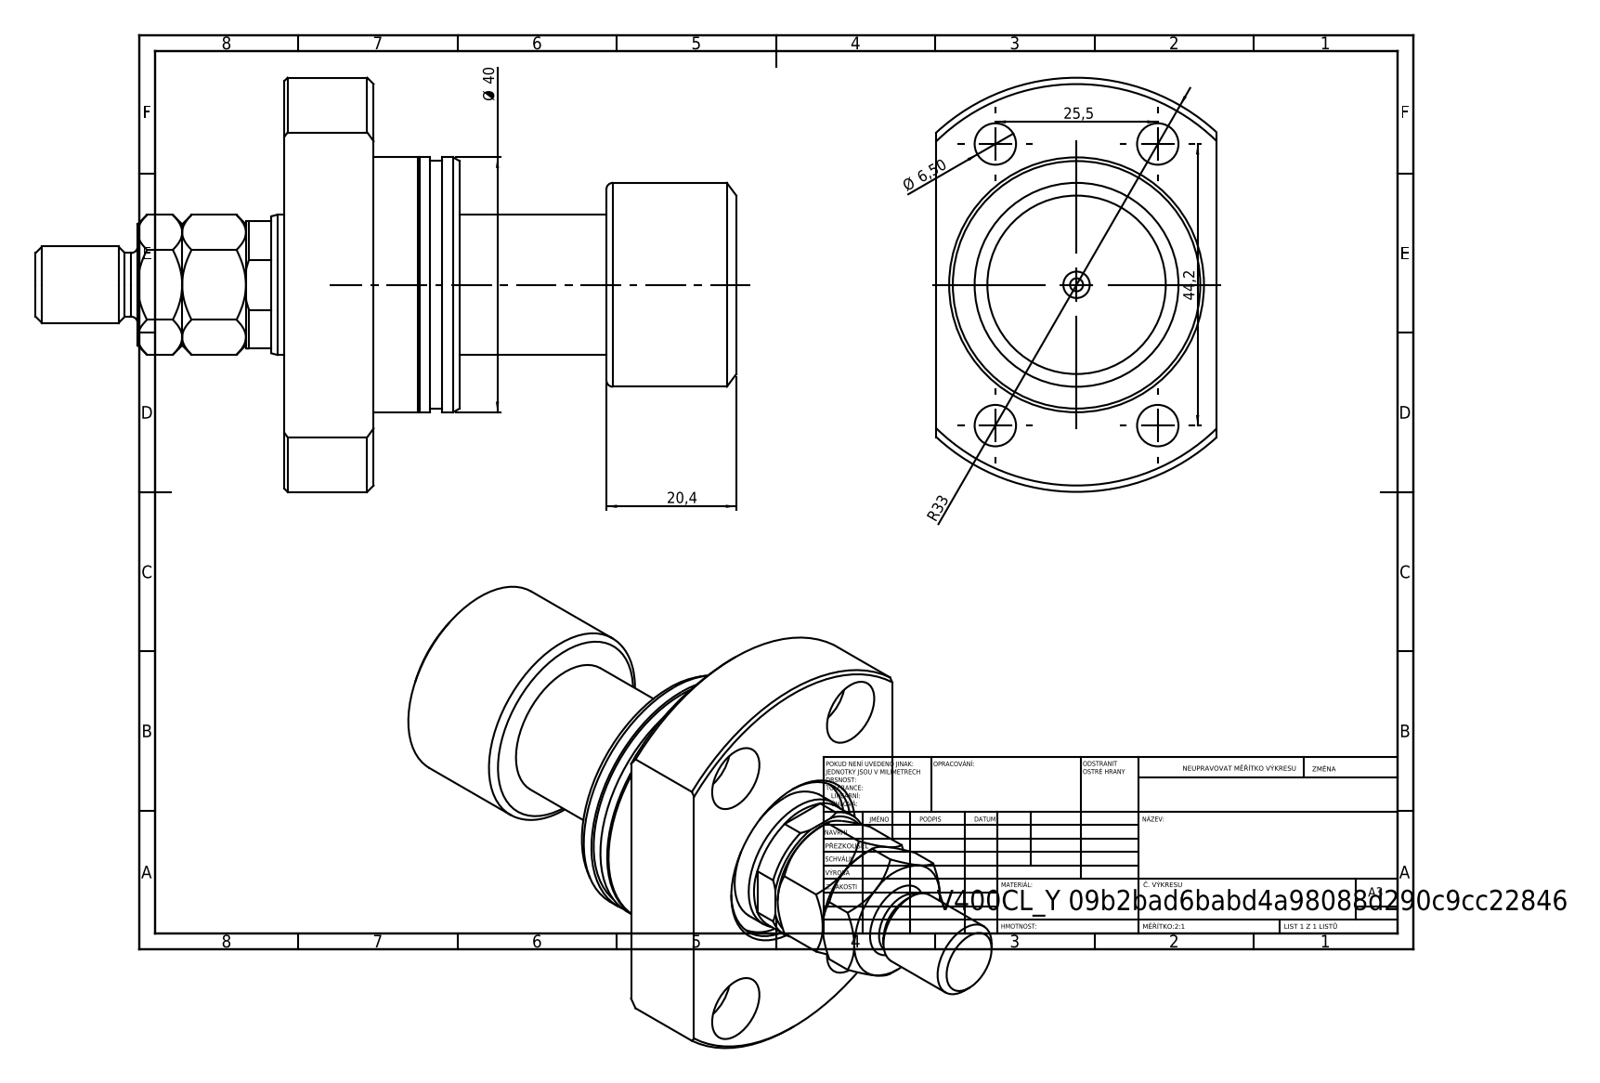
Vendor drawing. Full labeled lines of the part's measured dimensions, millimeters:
Part name (STEP PRODUCT): V400CL_PC_Y; V400CL_VC_X; MTA
STEP written by: SolidWorks 2019 (CONFIG_CONTROL_DESIGN)
Units: millimetres
Bodies: 3 solids, 152 faces (41 planar, 51 cylindrical, 60 other)
Overall size (bounding box): 110 × 65 × 44
Volume: 83 374 mm³ · Surface area: 22 153 mm²
Round holes (diameter × count): ⌀6.5 ×4, ⌀10.5 ×4, ⌀2.05 ×1, ⌀5 ×1, ⌀6 ×1, ⌀22 ×1, ⌀26.5 ×1
Round bosses / shafts (diameter × count): ⌀40 ×1, ⌀39 ×1, ⌀32 ×1, ⌀12 ×1, ⌀10 ×1
Partial cylindrical surfaces — rounded edges, fillets, slot ends (radius × count): R10.75 ×1, R32.5 ×1
Main face-to-face distances: 14, 13.5, 27.5, 44, 43.45, 56.95, 70.95, 77, 33.55, 20.05
Hole centre spacings: 25.51, 25.5, 44.2, 51.03
